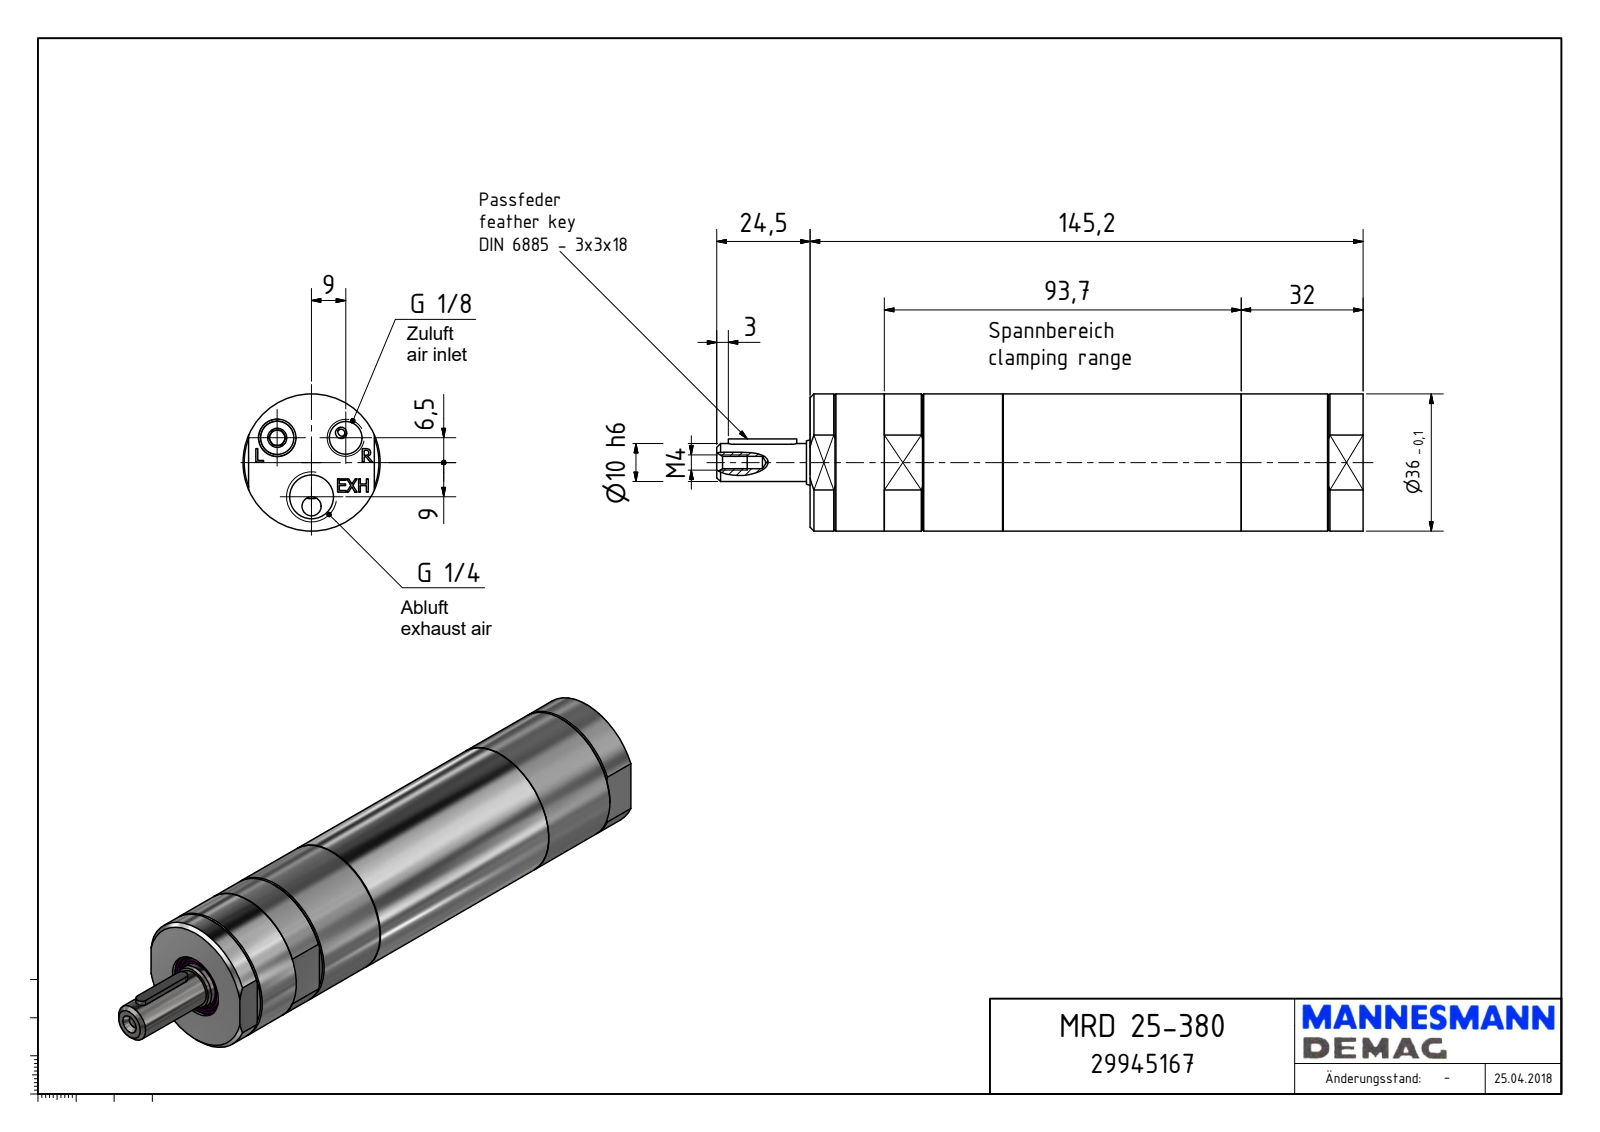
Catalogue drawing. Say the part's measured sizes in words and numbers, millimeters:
The part is named "MRD 25-380_29945167". Its 3-D file was written by "Autodesk Inventor 2018 (AUTOMOTIVE_DESIGN)". It is 1 solid with 175 faces: 107 planar, 33 cylindrical and 35 other. Overall it measures 169.7 by 36 by 36 millimeters. Its volume is 146 547 cubic millimeters and its surface area 21 525 square millimeters. Round holes: 2 of diameter 8.57, 1 of diameter 3.24, 1 of diameter 4, 1 of diameter 11.45, 1 of diameter 15.5, 1 of diameter 17. Round bosses or shafts: 1 of diameter 36, 1 of diameter 32, 1 of diameter 11.95, 1 of diameter 10. Partial cylindrical surfaces (rounded edges, fillets, slot ends): 2 of radius 1.5, 2 of radius 4, 1 of radius 14.68, 1 of radius 15.5, 1 of radius 16.51. The main face-to-face distances are 145.2, 33, 50.7, 94.5, 50.5, 94.7, 134.46, 83.96, 83.76, 10.74. The hole center spacings are 11.1, 17.92, 9, 18.
